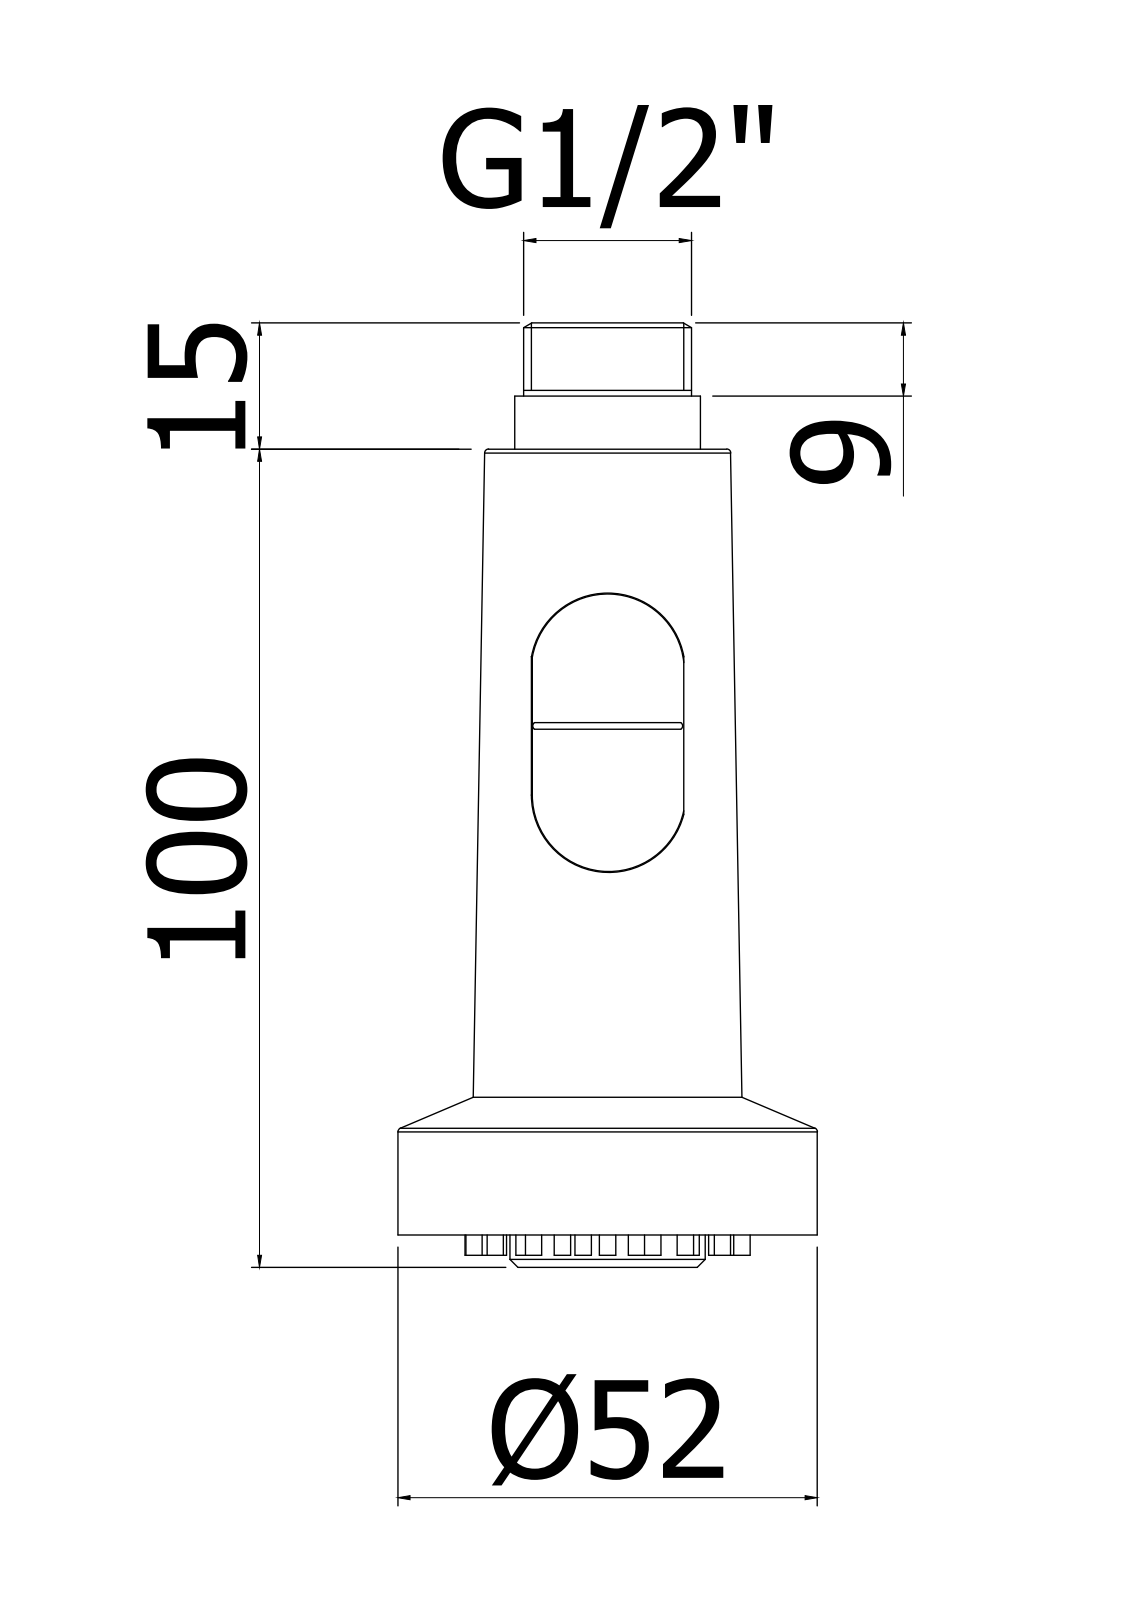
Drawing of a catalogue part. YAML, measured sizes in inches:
part_name: "ZDOC049CR"
step_written_by: "CREO PARAMETRIC BY PTC INC, 2020044 (CONFIG_CONTROL_DESIGN)"
units: inches
bodies: {solids: 0, faces: 224, planar: 59, cylindrical: 149, other: 16}
overall_size: [4.547, 2.028, 2.028]
round_holes:
  - {diameter: 0.039, count: 32}
  - {diameter: 0.598, count: 1}
  - {diameter: 0.72, count: 1}
round_bosses_or_shafts:
  - {diameter: 0.079, count: 32}
  - {diameter: 2.028, count: 1}
  - {diameter: 0.945, count: 1}
  - {diameter: 0.898, count: 1}
  - {diameter: 0.819, count: 1}
partial_cylinders:
  - {radius: 0.02, count: 2}
  - {radius: 0.374, count: 2}
  - {radius: 0.004, count: 1}
  - {radius: 0.079, count: 1}
  - {radius: 0.4, count: 1}
face_to_face_distances: [0.079, 0.15, 0.154, 3.949, 3.799, 3.795, 0.157, 3.87, 3.72, 3.717]
hole_center_spacings: [0.571, 0.223, 0.437, 0.634, 0.776, 1.098, 1.22, 0.142]
